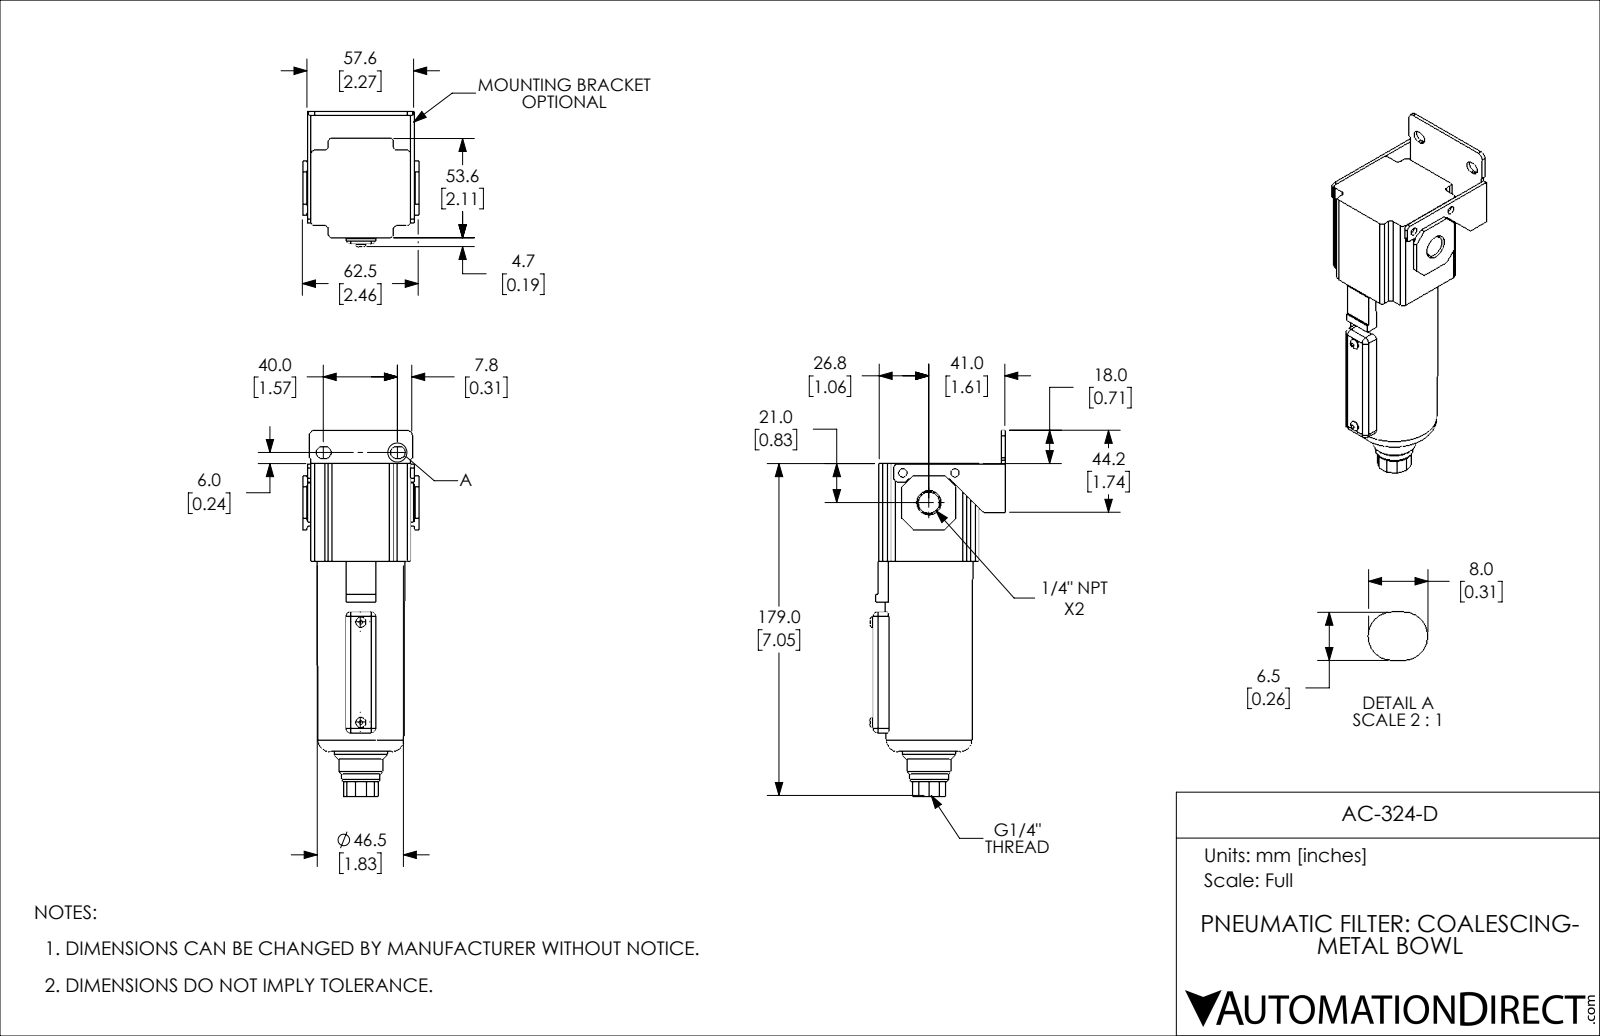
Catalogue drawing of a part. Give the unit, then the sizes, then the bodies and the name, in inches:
Units: inches
Overall size (bounding box): 7.756 × 2.854 × 2.461
Round holes (diameter × count): ⌀0.177 ×2, ⌀0.451 ×2
Round bosses / shafts (diameter × count): ⌀0.217 ×2, ⌀1.102 ×1, ⌀0.906 ×1, ⌀0.787 ×1
Partial cylindrical surfaces — rounded edges, fillets, slot ends (radius × count): R0.079 ×15, R0.098 ×8, R0.128 ×4, R0.039 ×2, R0.118 ×2
Main face-to-face distances: 0.079, 2.11, 2.189, 0.559, 2.669, 0.48, 2.591, 0.096, 0.175, 2.285
Hole centre spacings: 0.837, 1.102
Volume: 20.47 in³ · Surface area: 67.02 in²
Bodies: 1 solid, 200 faces (116 planar, 60 cylindrical, 24 other)
Part name (STEP PRODUCT): AC-324-D
STEP written by: SolidWorks 2018 (AUTOMOTIVE_DESIGN)
